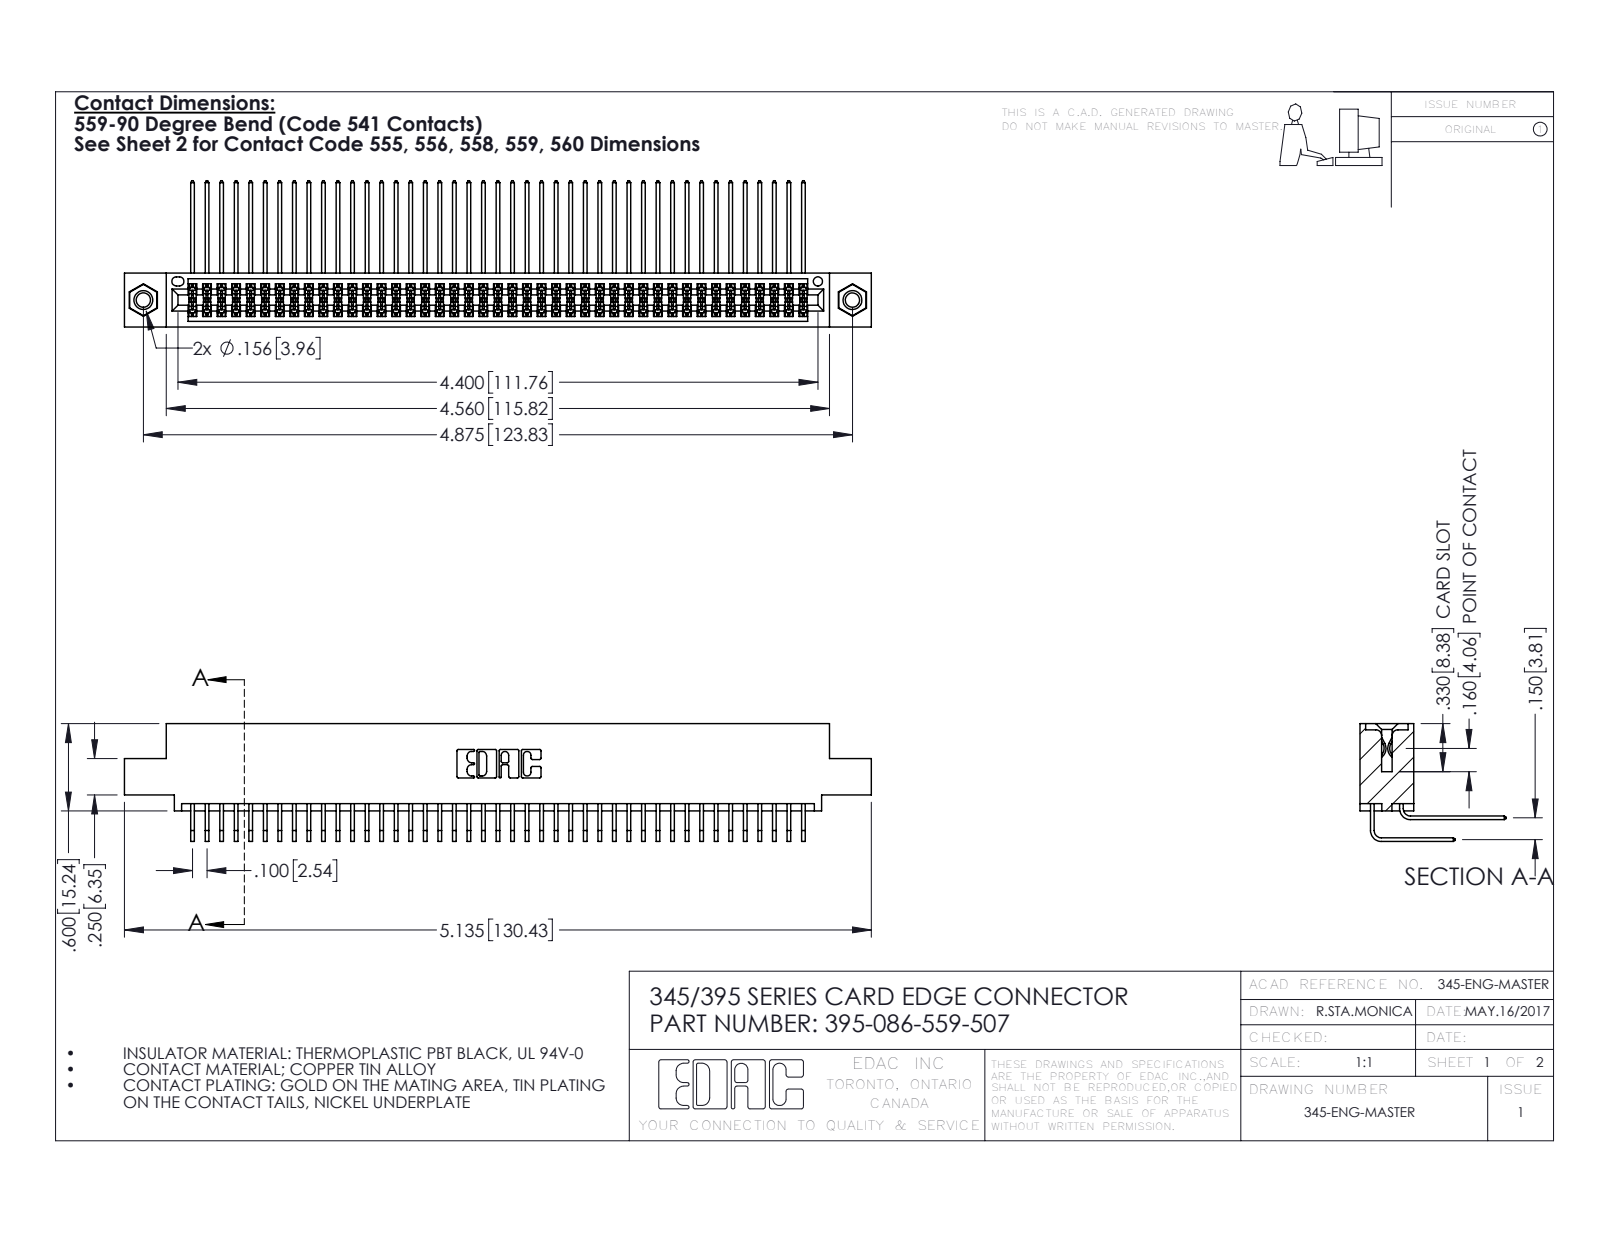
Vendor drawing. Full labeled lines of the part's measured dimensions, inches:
Part name (STEP PRODUCT): 345 Part_0.110 Offset - 0.156 Dia-TI; 345-250-001_345-250-005-103; 395-086-559-507; 345-292-001_558 559 Tail - 1 (+1 more)
STEP written by: SolidWorks 2016 (CONFIG_CONTROL_DESIGN)
Units: inches
Bodies: 89 solids, 4662 faces (3126 planar, 1520 cylindrical, 16 other)
Overall size (bounding box): 5.135 × 1.005 × 0.809
Volume: 0.799 in³ · Surface area: 33.82 in²
Round holes (diameter × count): ⌀0.098 ×2, ⌀0.125 ×2, ⌀0.156 ×2, ⌀0.064 ×1
Round bosses / shafts (diameter × count): ⌀0.155 ×2
Partial cylindrical surfaces — rounded edges, fillets, slot ends (radius × count): R0.006 ×130, R0.01 ×22, R0.007 ×6, R0.031 ×6, R0.026 ×3, R0.014 ×2, R0.019 ×2, R0.022 ×2
Main face-to-face distances: 0.072, 0.298, 0.2, 0.37, 0.098, 0.272, 0.025, 0.225, 0.175, 0.15
Hole centre spacings: 0.27, 4.639, 4.875
